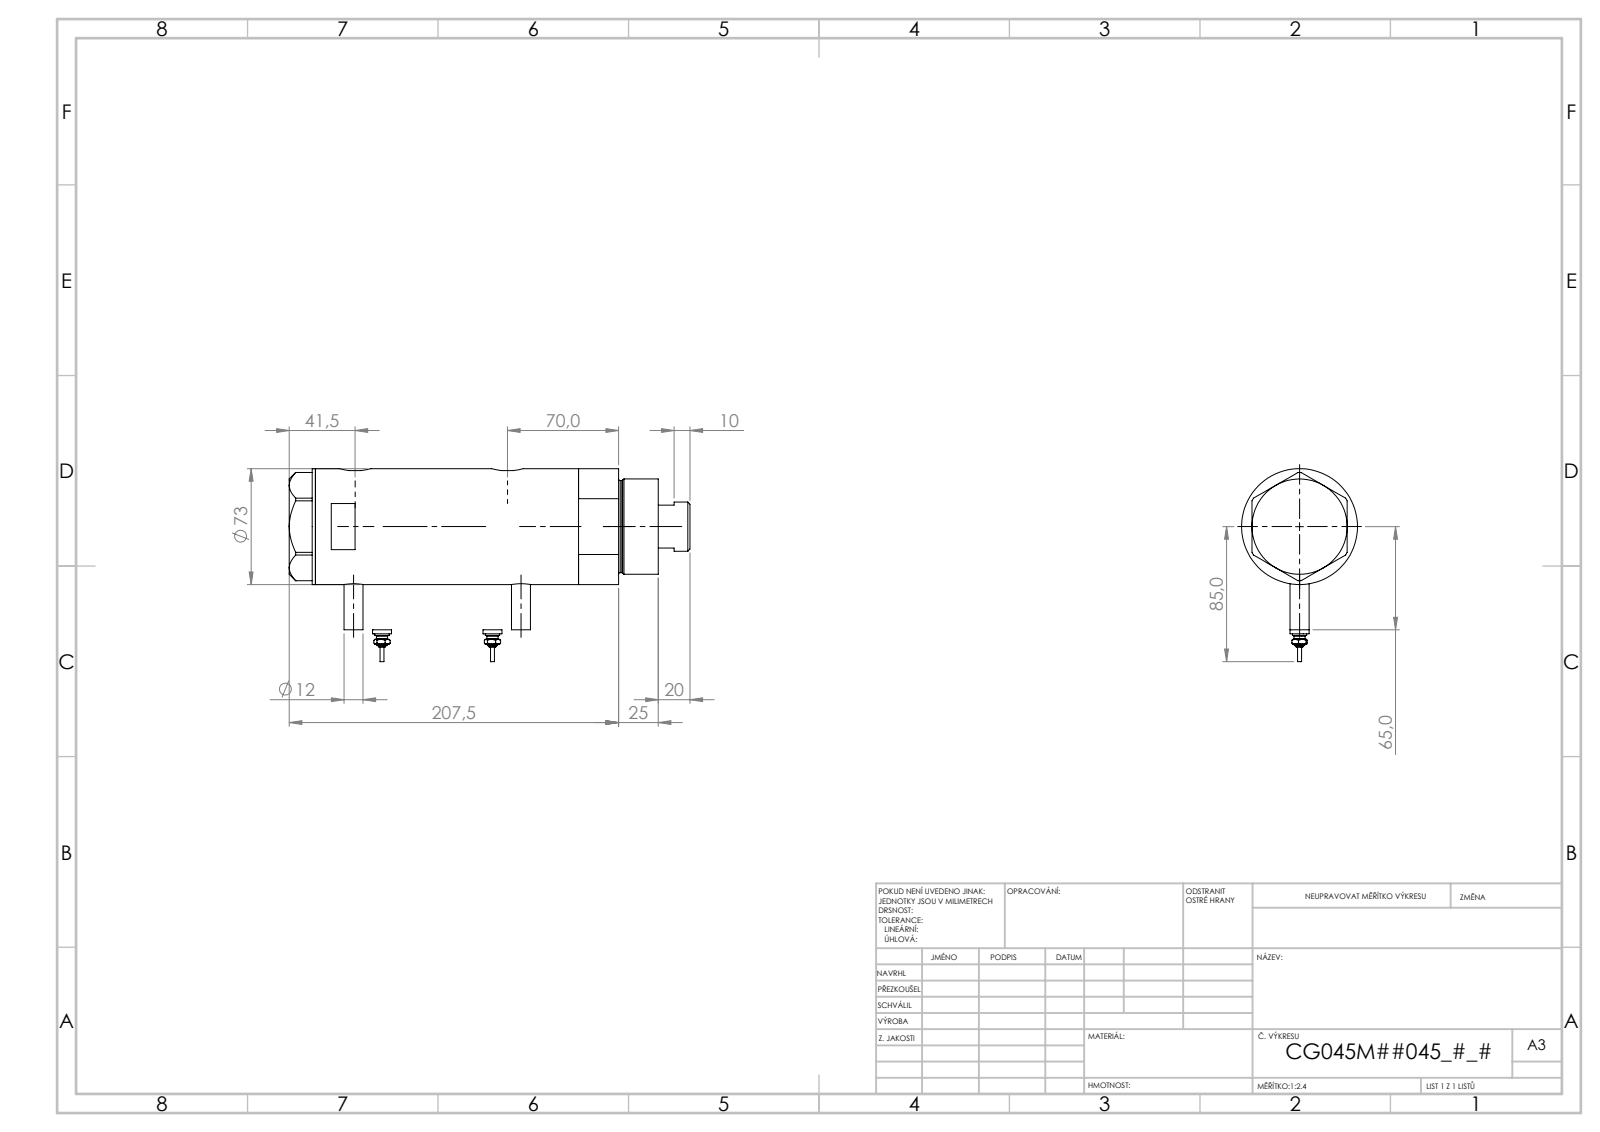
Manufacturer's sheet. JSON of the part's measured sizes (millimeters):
{"part_name": "V270CG_FRONT; V270CG_SWITCH; V270CG_MIDDLE; V270CG_VC (+1 more)", "step_written_by": "SolidWorks 2019 (CONFIG_CONTROL_DESIGN)", "units": "millimeters", "bodies": {"solids": 6, "faces": 231, "planar": 78, "cylindrical": 79, "other": 74}, "overall_size": [236.52, 105.3, 73], "volume_mm3": 822576, "surface_area_mm2": 143093, "round_holes": [[5, 2], [12.5, 2], [13.16, 2], [10.5, 1], [32, 1], [33.5, 1], [45, 1], [48, 1], [64, 1]], "round_bosses_or_shafts": [[12, 3], [9, 2], [7, 2], [4.34, 2], [2.4, 2], [73, 1], [60, 1], [58, 1]], "partial_cylinders_radius": [[10, 2]], "face_to_face_distances": [112.14, 26, 86.14, 16.5, 42.5, 128.64, 200.01, 216.51, 174.01, 87.87], "hole_center_spacings": [96.65, 0.99, 1, 8.5, 8.51, 87.15, 88.14, 88.15]}
